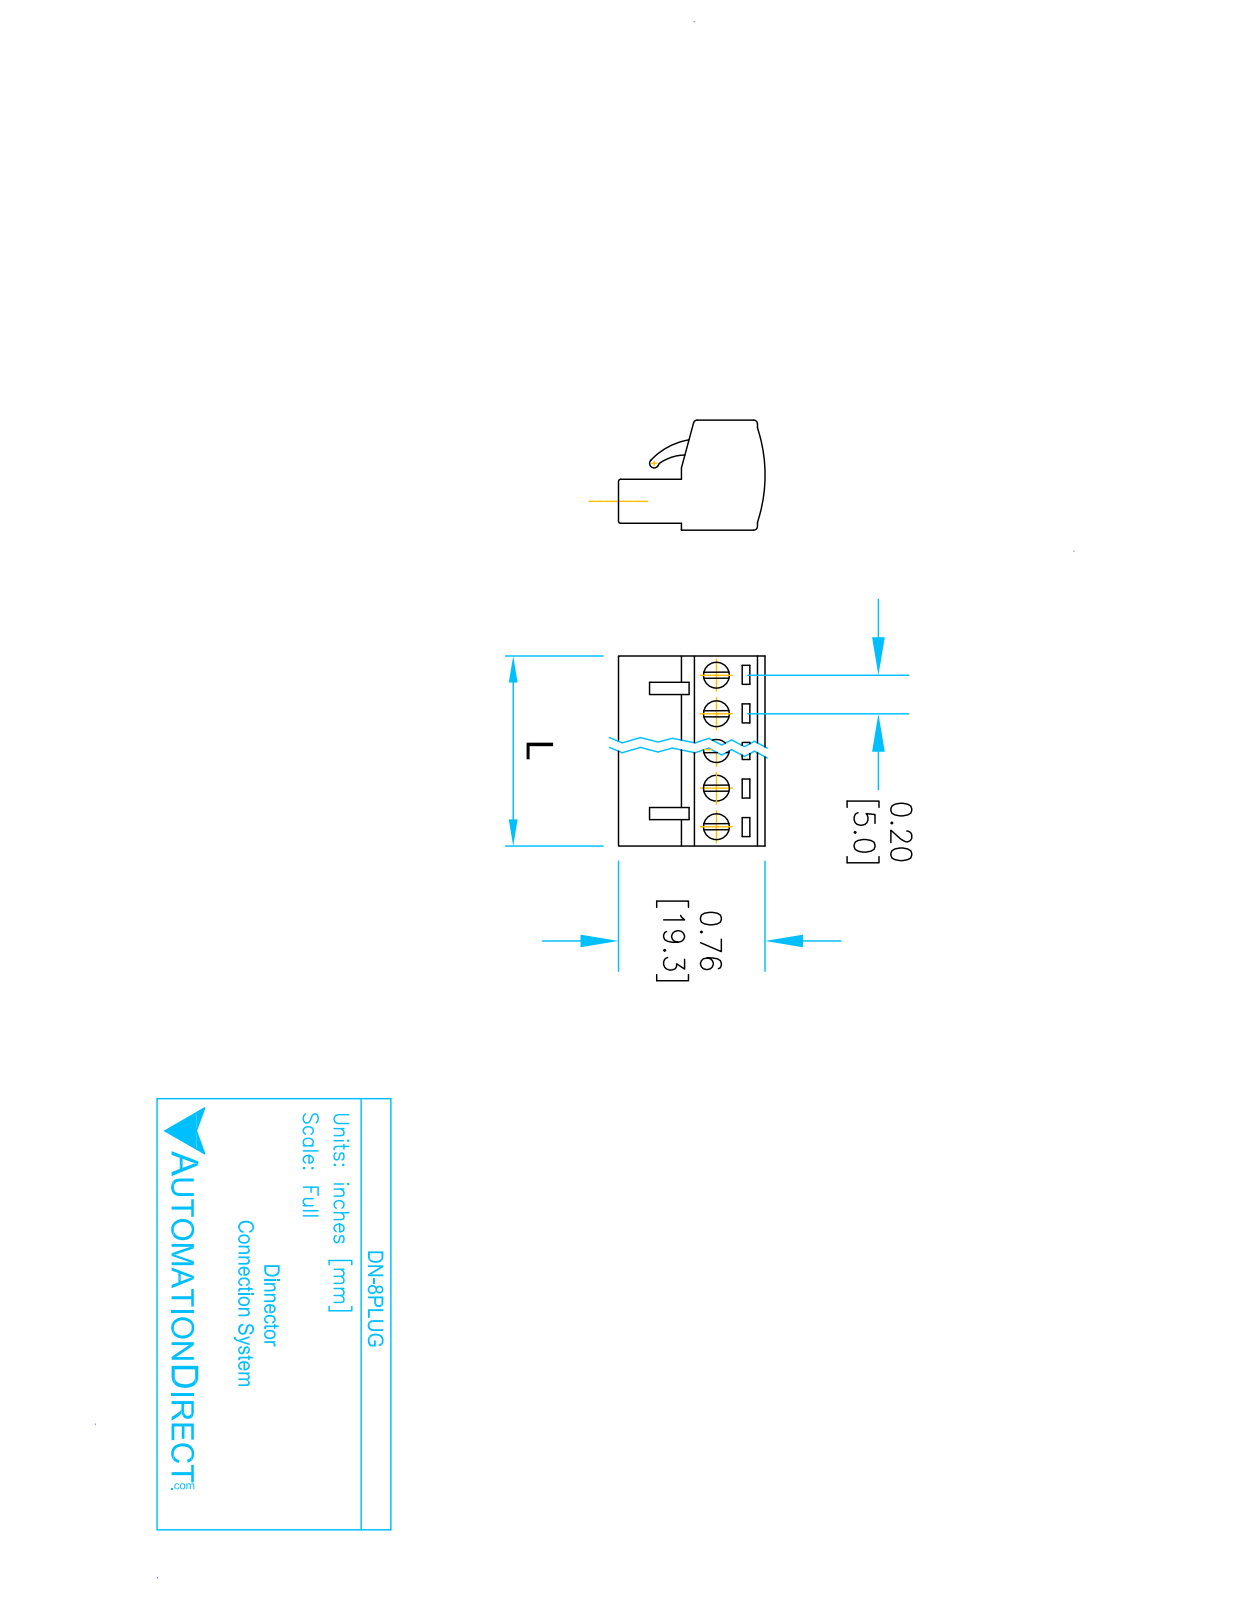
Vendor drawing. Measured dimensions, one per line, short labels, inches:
name: 49001_S; 49008_S; 49002_S; 49001_S_49002_SENZA DENTE
written by: SolidWorks 2013 (AUTOMOTIVE_DESIGN)
unit: in
bodies: 7 solids, 728 faces (511 planar, 177 cylindrical, 40 other)
size: 1.6 × 0.76 × 0.571
volume: 0.424 in³; area: 11.07 in²
holes: 8× ⌀0.063, 8× ⌀0.098, 8× ⌀0.134, 8× ⌀0.142
bosses: 8× ⌀0.118
rounds: 8× R0.114, 3× R0.02, 2× R0.012, 1× R0.024, 1× R0.236, 1× R0.354, 1× R0.789
face distances: 0.2, 0.4, 0.6, 0.8, 1, 1.2, 0.264, 0.039, 0.571, 0.307
hole spacings: 0.2, 0.4, 0.6, 0.8, 1, 1.2, 1.4
